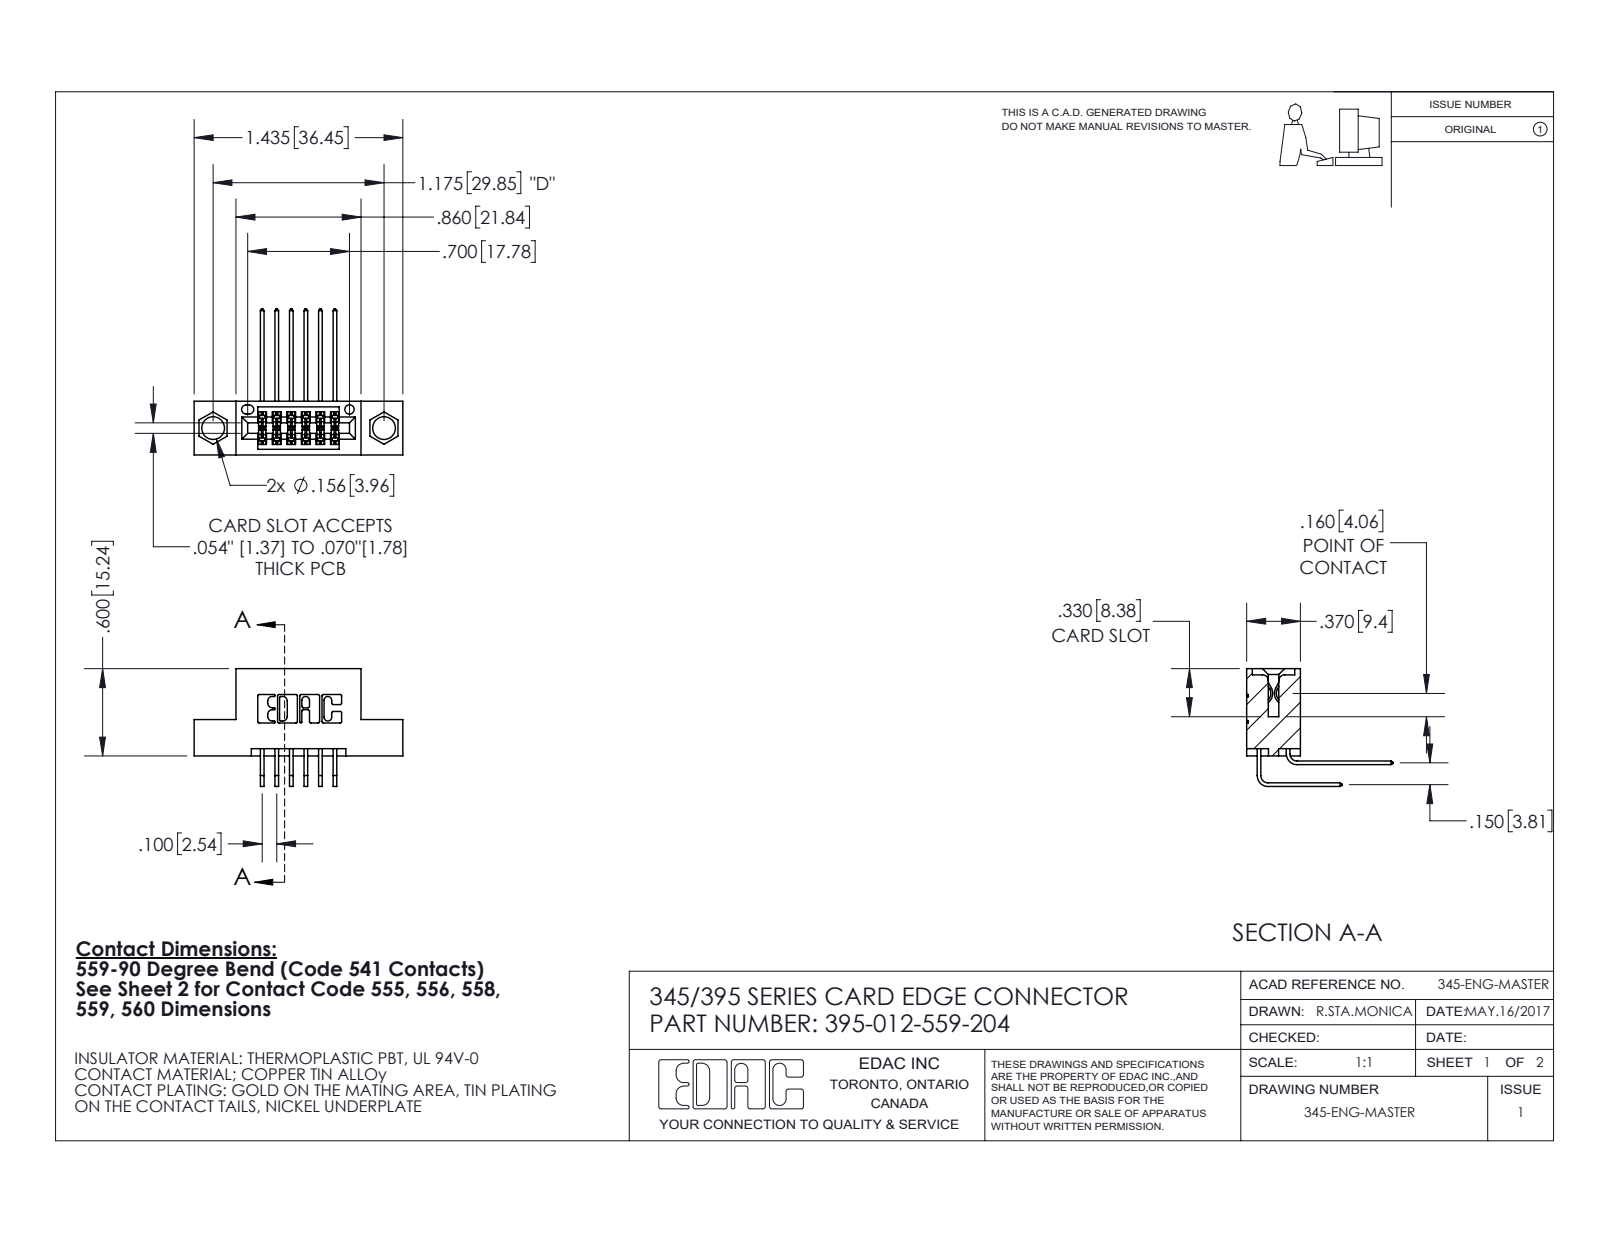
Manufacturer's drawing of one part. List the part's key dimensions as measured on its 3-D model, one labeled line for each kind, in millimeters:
Part name (STEP PRODUCT): 345-292-001_559 Tail - 2; 395-012-559-204; 345 Part_Flush Mounting Lugs - 0.156 Dia-TI; 345-292-001_558 559 Tail - 1
STEP written by: SolidWorks 2020 (CONFIG_CONTROL_DESIGN)
Units: millimetres
Bodies: 13 solids, 764 faces (514 planar, 250 cylindrical, 0 other)
Overall size (bounding box): 36.4 × 25.5 × 20.5
Volume: 3 160 mm³ · Surface area: 4 165 mm²
Round holes (diameter × count): ⌀4 ×2, ⌀1.6 ×1
Partial cylindrical surfaces — rounded edges, fillets, slot ends (radius × count): R0.3 ×22, R0.2 ×18, R0.2 ×6, R0.8 ×6, R0.7 ×3, R0.4 ×2, R0.5 ×2, R0.6 ×2
Main face-to-face distances: 5.1, 2.5, 1.8, 7.6, 9.4, 2.5, 6.9, 0.6, 3.8, 7.6
Hole centre spacings: 6.9, 24, 29.8
